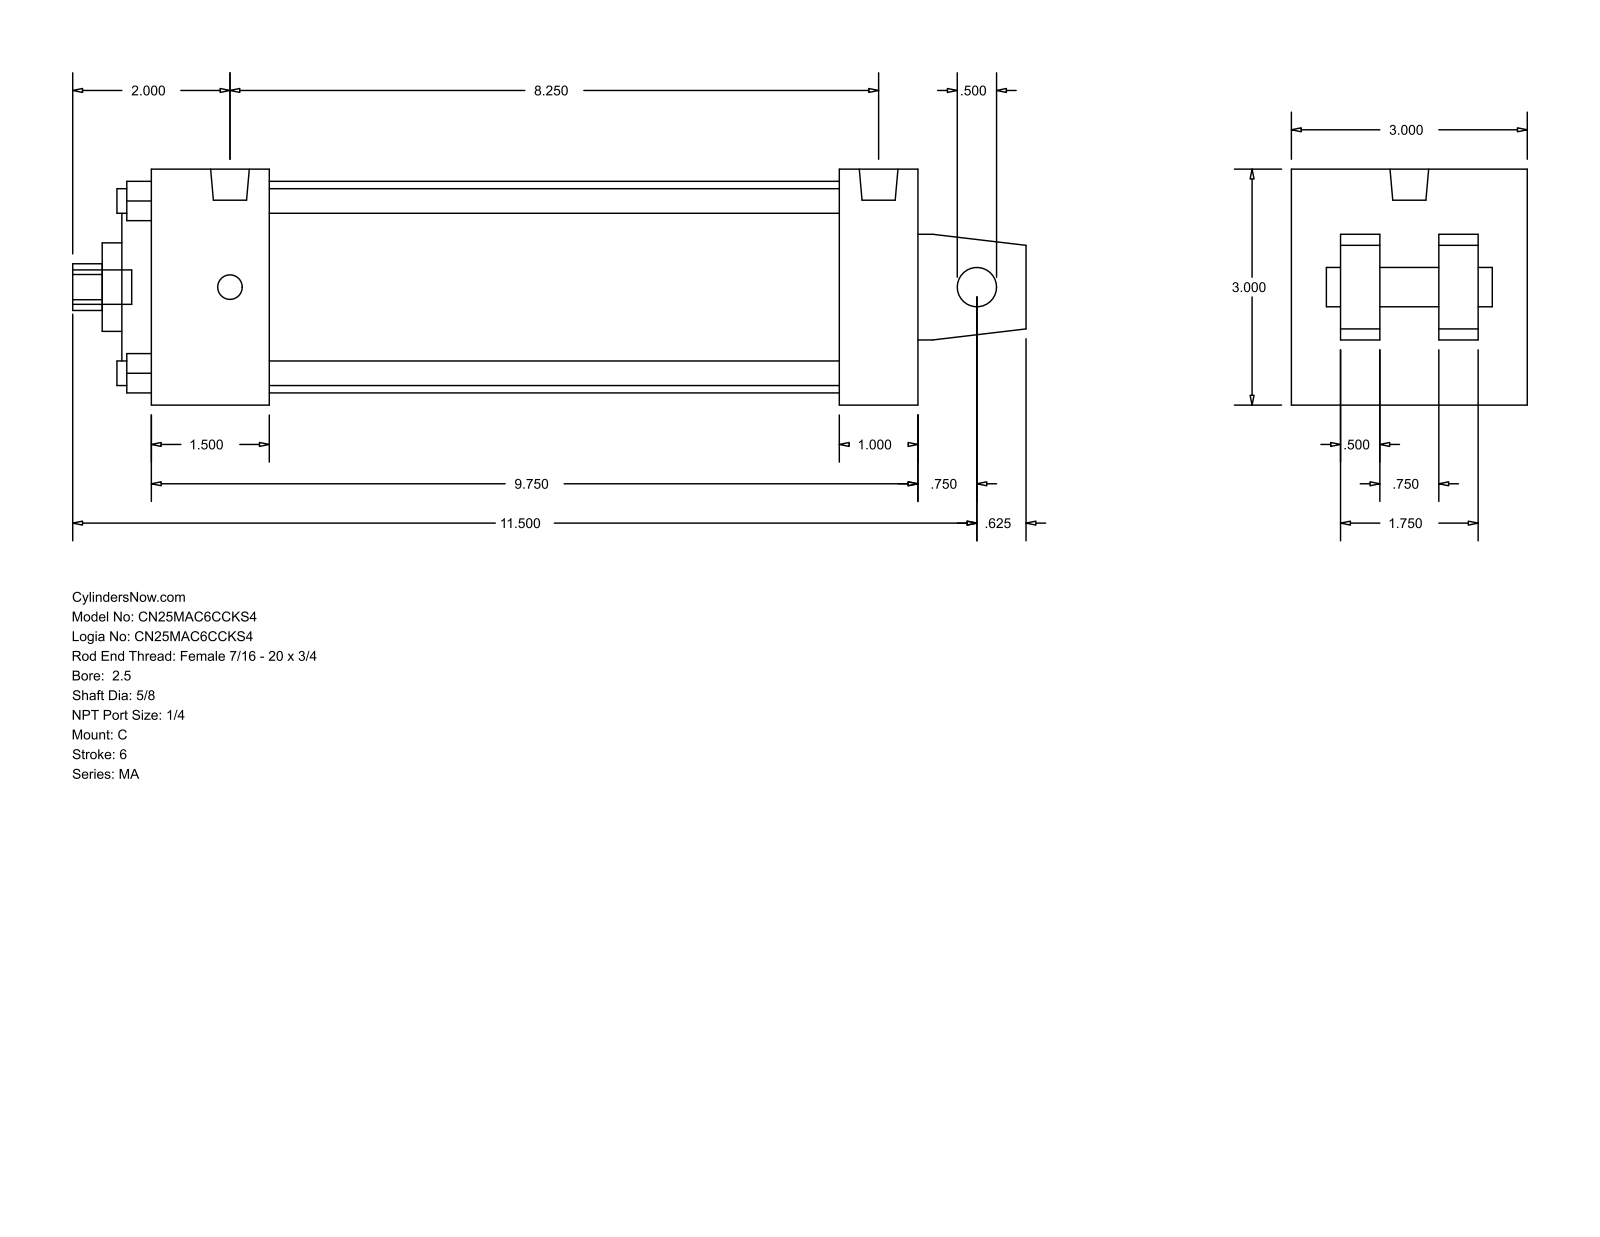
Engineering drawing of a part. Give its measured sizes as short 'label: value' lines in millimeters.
name: MA_C__0250_0.625
written by: GSSL Pune (CONFIG_CONTROL_DESIGN)
unit: mm
bodies: 0 solids, 105 faces (77 planar, 28 cylindrical, 0 other)
size: 307.98 × 76.2 × 76.2
holes: 4× ⌀7.94, 1× ⌀12.7, 1× ⌀15.88, 1× ⌀28.57, 1× ⌀50.8, 1× ⌀68.33
bosses: 4× ⌀7.94, 2× ⌀12.49, 1× ⌀11.11
rounds: 1× R7.54
face distances: 76.2, 247.65, 12.7, 15.87, 60.33, 47.63, 25.4, 38.1, 222.25, 184.15
hole spacings: 39.33, 55.62, 78.66
